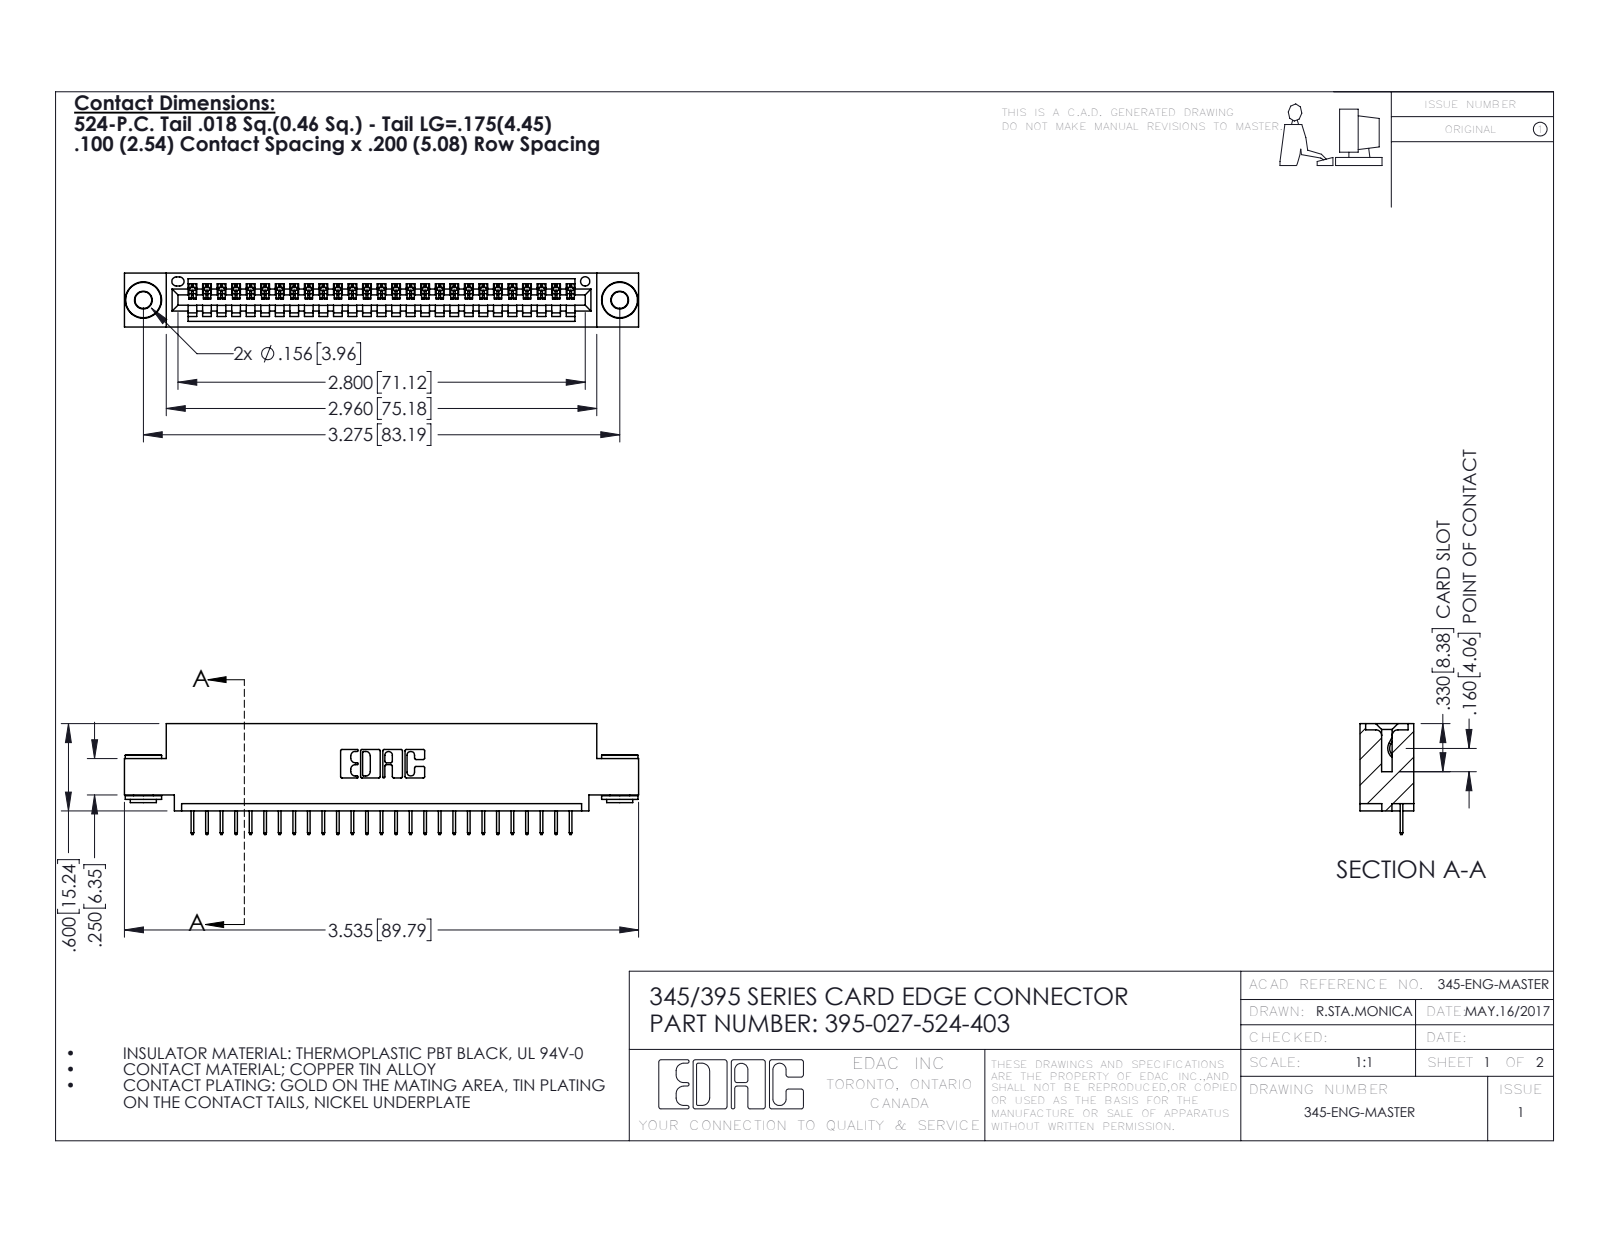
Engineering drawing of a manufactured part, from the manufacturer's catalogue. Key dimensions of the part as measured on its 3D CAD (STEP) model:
Part name (STEP PRODUCT): 395-027-524-403; 345 Part_0.110 Offset - 0.156 Dia-TH; 345-250-002_345-250-002-102; 345-292-001_345-293-124
STEP written by: SolidWorks 2016 (CONFIG_CONTROL_DESIGN)
Units: inches
Bodies: 30 solids, 1842 faces (1336 planar, 498 cylindrical, 8 other)
Overall size (bounding box): 3.535 × 0.762 × 0.37
Volume: 0.503 in³ · Surface area: 16.6 in²
Round holes (diameter × count): ⌀0.116 ×2, ⌀0.156 ×2, ⌀0.064 ×1
Round bosses / shafts (diameter × count): ⌀0.25 ×2, ⌀0.18 ×2, ⌀0.136 ×2
Partial cylindrical surfaces — rounded edges, fillets, slot ends (radius × count): R0.006 ×54, R0.01 ×22, R0.007 ×6, R0.031 ×6, R0.026 ×3, R0.031 ×2, R0.04 ×2, R0.014 ×1
Main face-to-face distances: 0.072, 0.298, 0.37, 0.2, 0.025, 0.098, 0.272, 0.225, 0.072, 0.149
Hole centre spacings: 0.27, 3.04, 3.275
